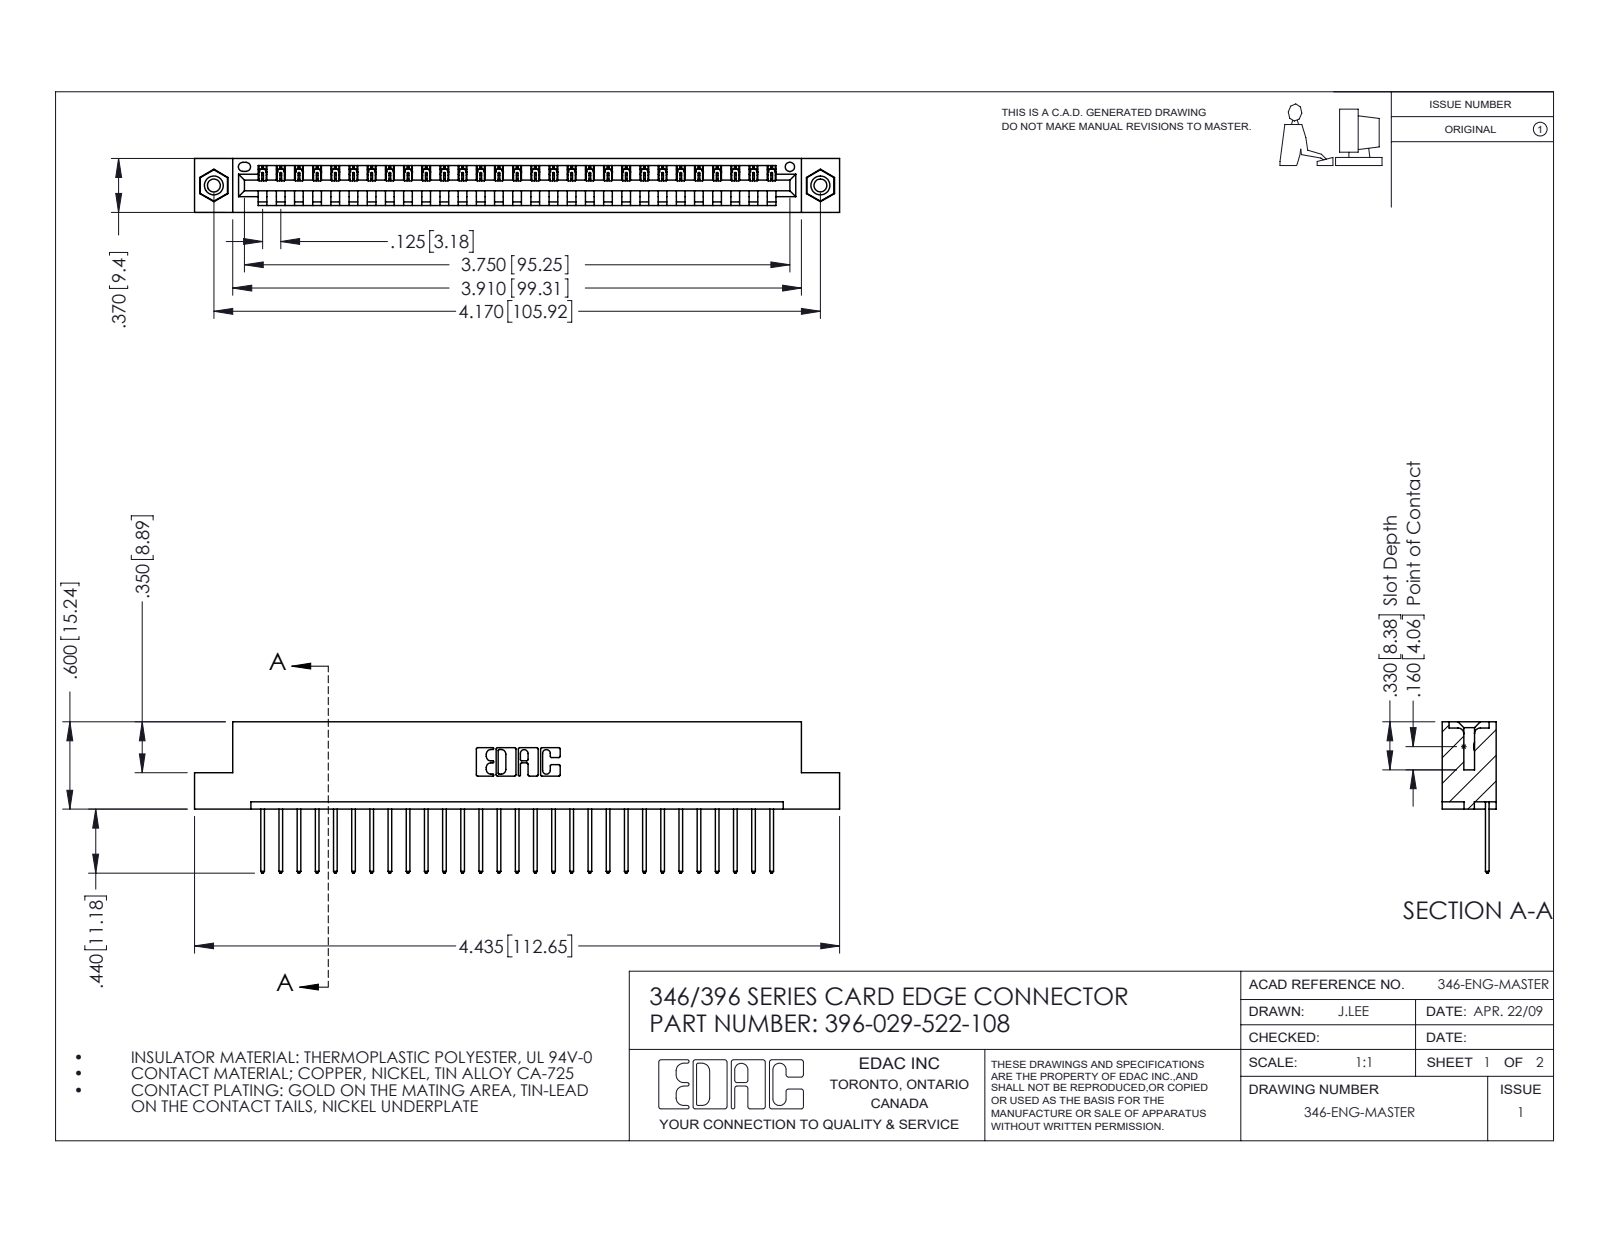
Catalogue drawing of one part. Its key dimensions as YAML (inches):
part_name: "346 Part_Flush Mounting Lugs - 0.156 Dia-TI; 396-029-522-108; 345-250-001_345-250-003-102; 345-292-001_345-293-122"
step_written_by: "SolidWorks 2016 (CONFIG_CONTROL_DESIGN)"
units: inches
bodies: {solids: 32, faces: 1864, planar: 1268, cylindrical: 580, other: 16}
overall_size: [4.435, 1.04, 0.37]
volume: 0.652
surface_area: 20.69
round_holes:
  - {diameter: 0.089, count: 2}
  - {diameter: 0.125, count: 2}
  - {diameter: 0.156, count: 2}
  - {diameter: 0.064, count: 1}
round_bosses_or_shafts:
  - {diameter: 0.155, count: 2}
partial_cylinders:
  - {radius: 0.006, count: 58}
  - {radius: 0.01, count: 58}
  - {radius: 0.01, count: 22}
  - {radius: 0.007, count: 6}
  - {radius: 0.031, count: 6}
  - {radius: 0.026, count: 3}
  - {radius: 0.031, count: 2}
  - {radius: 0.04, count: 2}
face_to_face_distances: [0.048, 0.322, 0.37, 0.25, 0.072, 0.298, 0.025, 0.148, 0.222, 0.1]
hole_center_spacings: [0.246, 3.962, 4.17]
